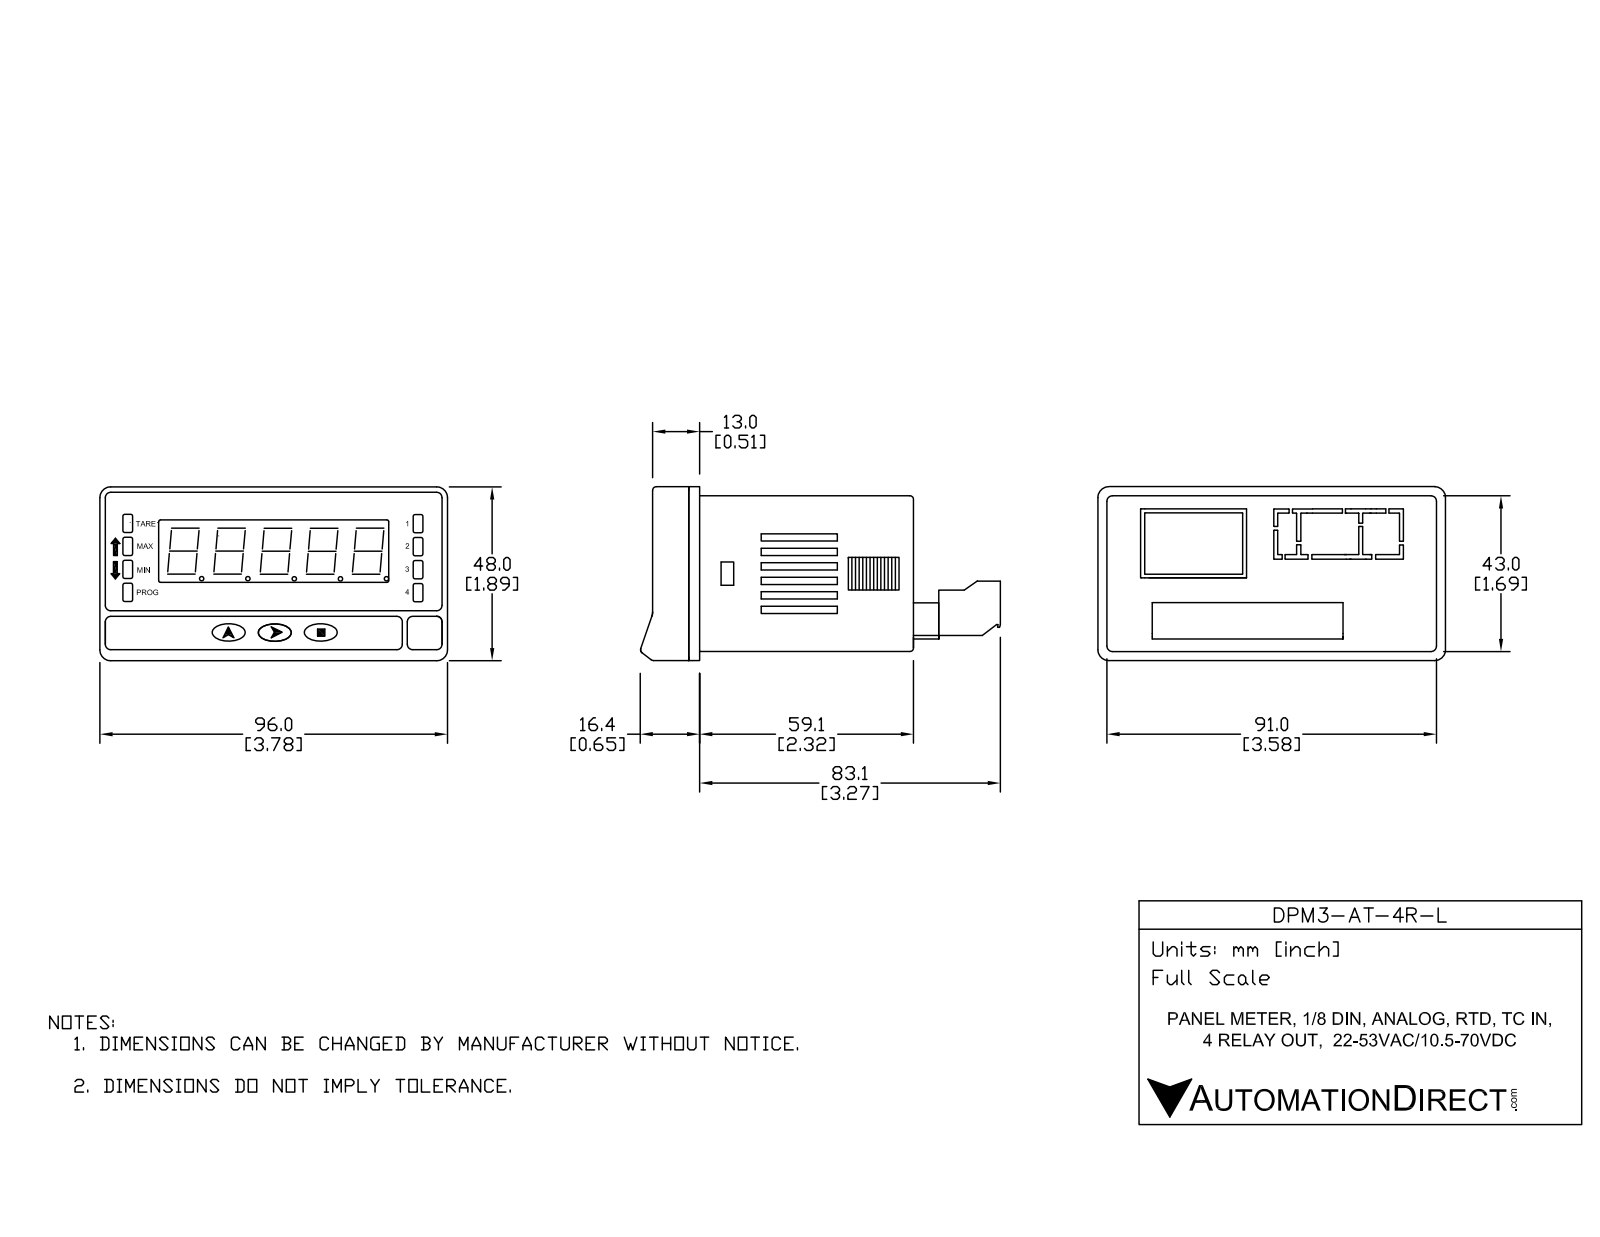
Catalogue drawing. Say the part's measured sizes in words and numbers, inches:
The part is named "DPM3-AT-4R-L". Its 3-D file was written by "SolidWorks 2017 (AUTOMOTIVE_DESIGN)". It is 10 solids with 2622 faces: 2041 planar, 368 cylindrical and 213 other. Overall it measures 3.916 by 3.78 by 1.89 inches. Its volume is 5.643 cubic inches and its surface area 104.7 square inches. Round holes: 12 of diameter 0.039, 12 of diameter 0.079, 10 of diameter 0.078, 10 of diameter 0.118, 10 of diameter 0.152. Round bosses or shafts: 5 of diameter 0.047. Partial cylindrical surfaces (rounded edges, fillets, slot ends): 53 of radius 0.004, 42 of radius 0.02, 24 of radius 0.012, 24 of radius 0.014, 12 of radius 0.07, 12 of radius 0.072, 10 of radius 0.118, 10 of radius 0.121. The main face-to-face distances are 0.059, 1.634, 0.098, 1.693, 1.575, 1.732, 3.524, 0.433, 0.157, 2.78. The hole center spacings are 0.138, 0.276, 0.201, 0.413, 0.748, 0.197, 0.197, 0.201.
